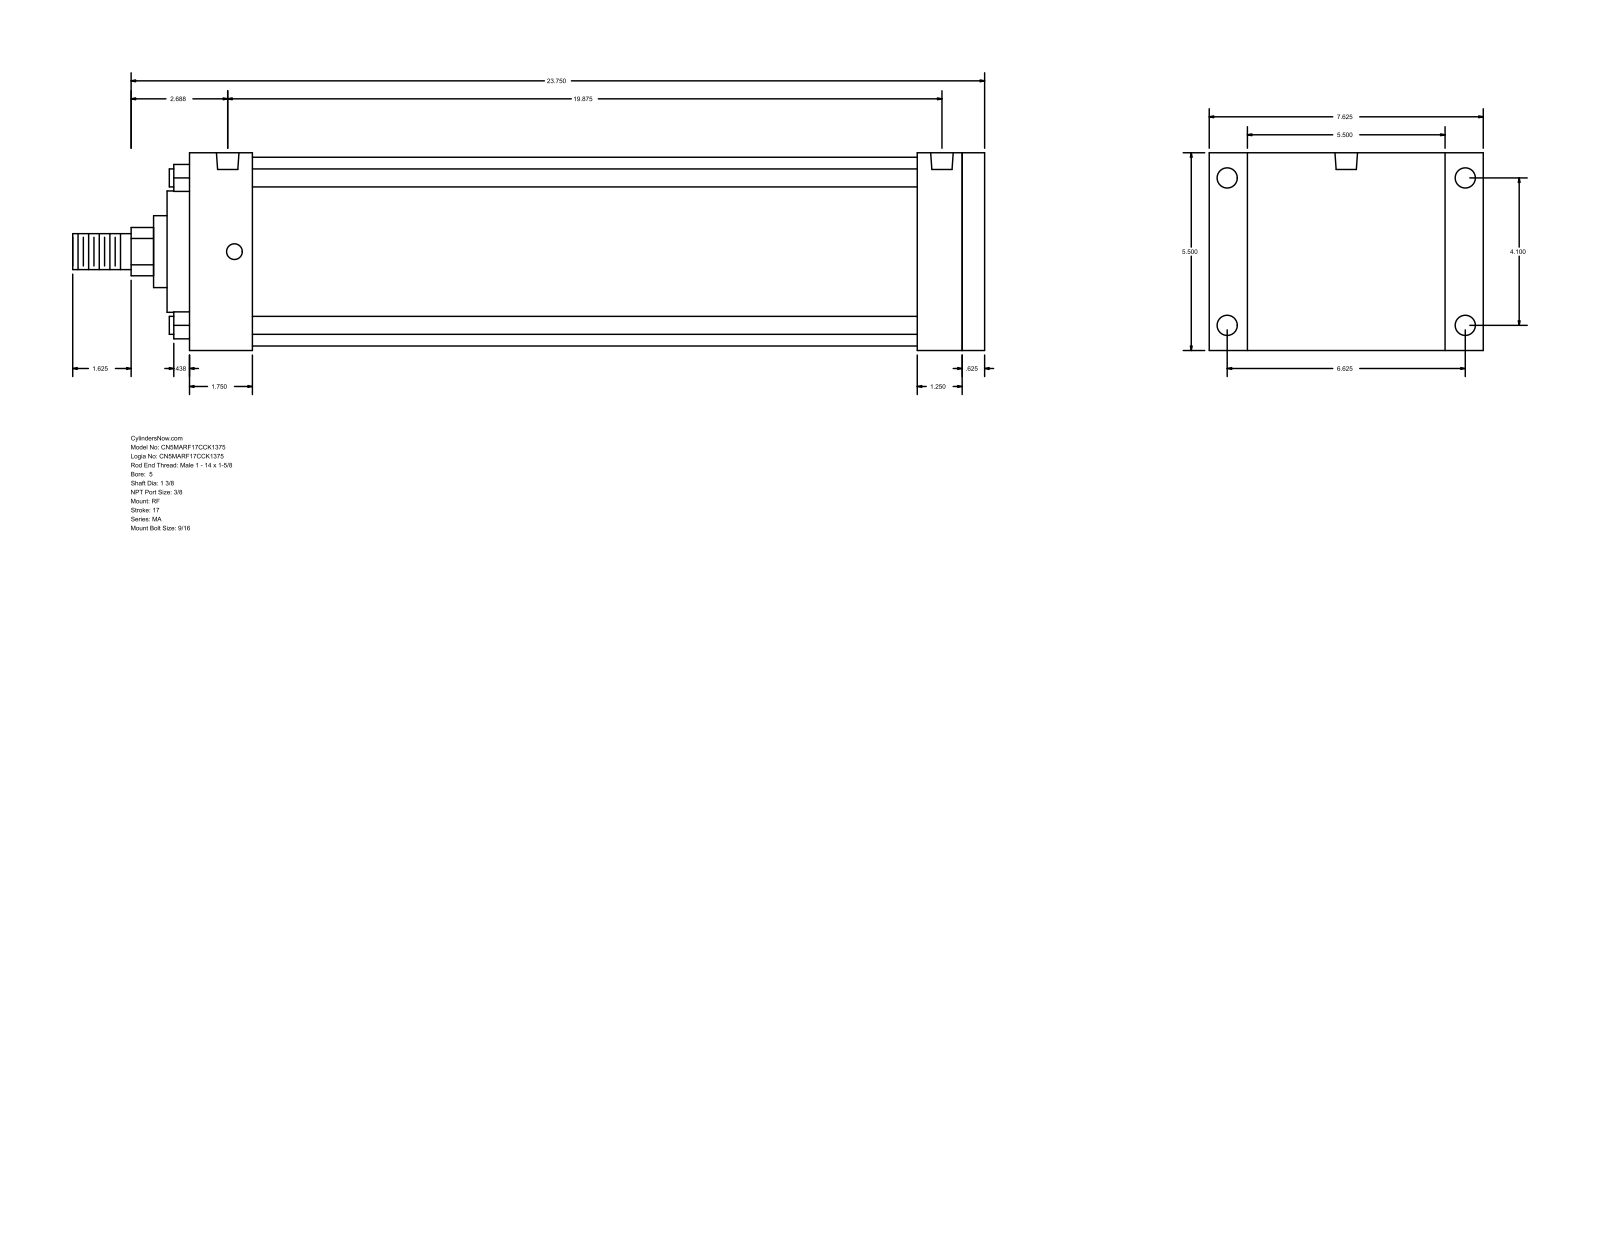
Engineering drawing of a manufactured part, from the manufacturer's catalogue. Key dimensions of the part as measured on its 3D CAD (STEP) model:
Part name (STEP PRODUCT): MA_RF__0500_1.375
STEP written by: GSSL Pune (CONFIG_CONTROL_DESIGN)
Units: millimetres
Bodies: 0 solids, 94 faces (65 planar, 29 cylindrical, 0 other)
Overall size (bounding box): 644.52 × 193.68 × 139.7
Round holes (diameter × count): ⌀11.11 ×4, ⌀14.29 ×4, ⌀15.93 ×2
Round bosses / shafts (diameter × count): ⌀12.7 ×4, ⌀133.35 ×1, ⌀85.72 ×1, ⌀50.8 ×1, ⌀34.92 ×1, ⌀25.4 ×1
Partial cylindrical surfaces — rounded edges, fillets, slot ends (radius × count): R17.06 ×1
Main face-to-face distances: 139.7, 561.98, 15.87, 546.11, 44.45, 501.66, 517.53, 514.35, 469.9, 31.76
Hole centre spacings: 104.14, 168.28, 197.9, 495.3, 4.76, 4.77, 500.06, 500.07
